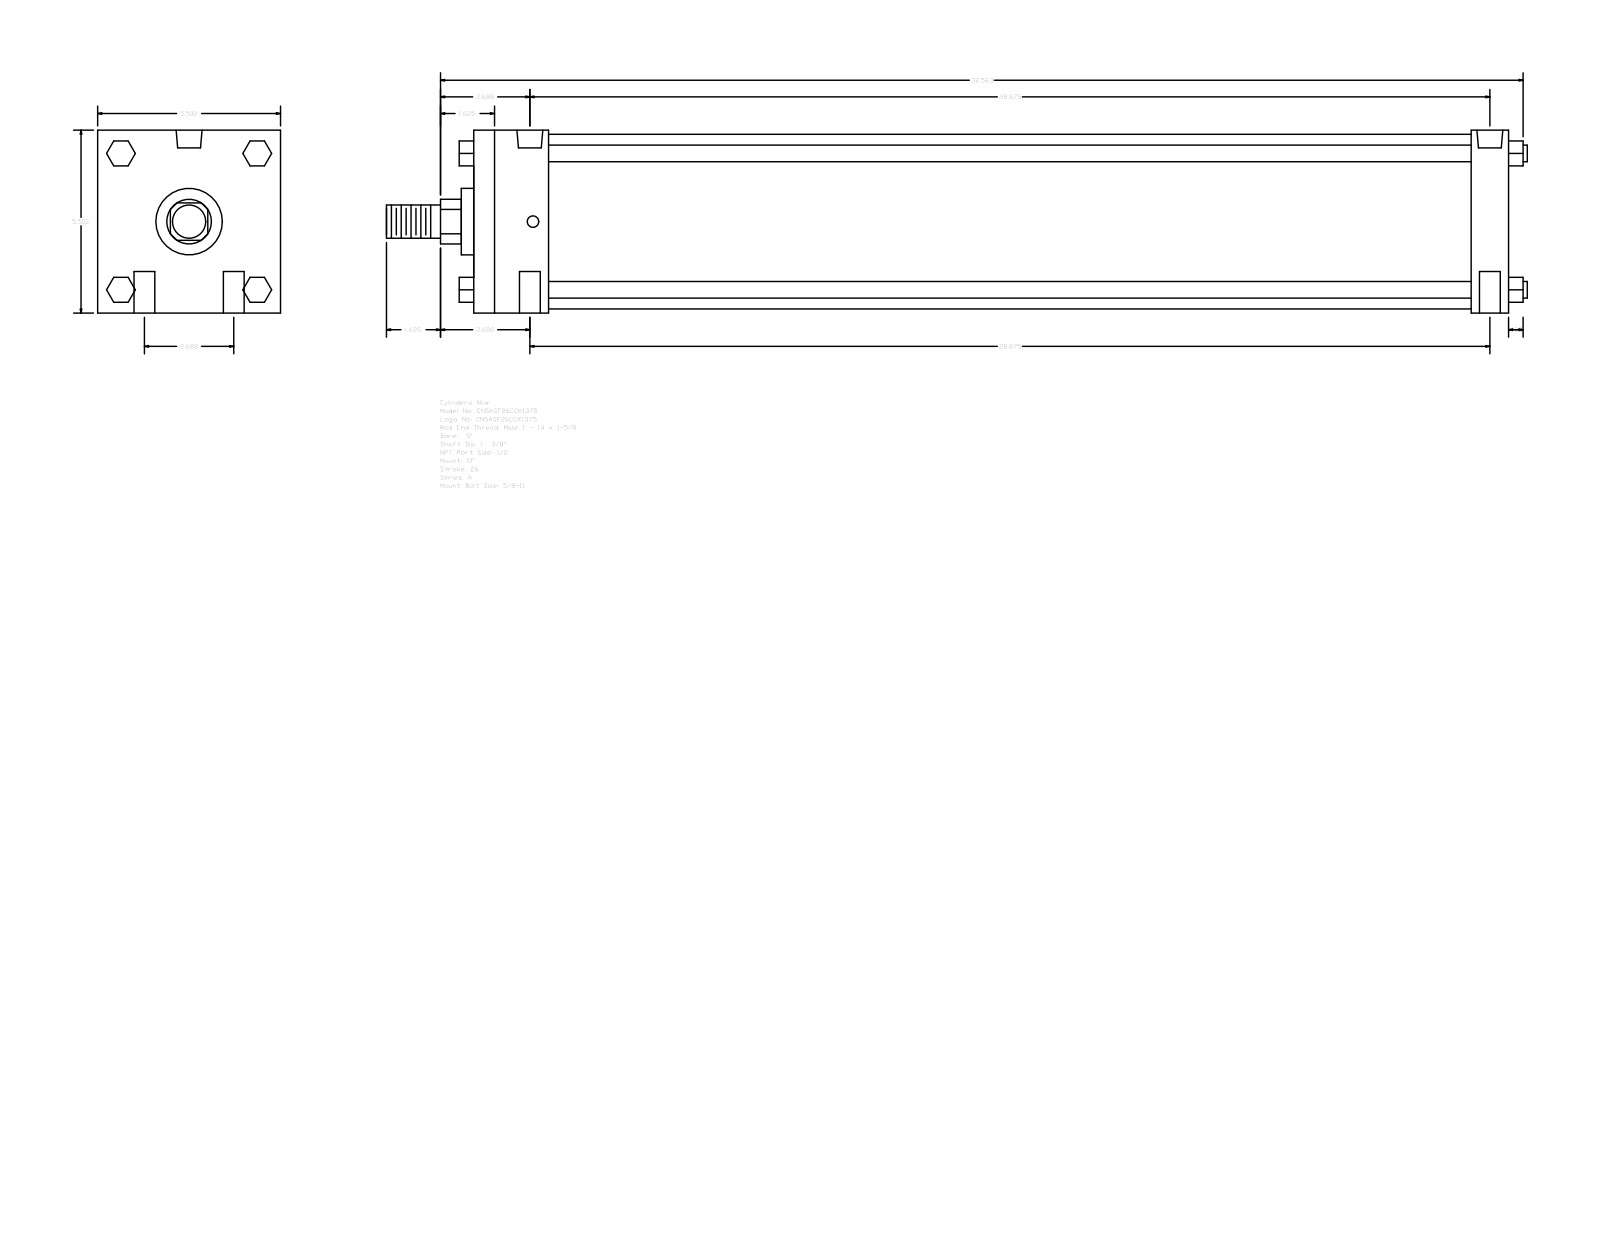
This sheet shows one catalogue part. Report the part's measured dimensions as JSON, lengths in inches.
{"part_name": "A_SF__0500_1.375", "step_written_by": "GSSL Pune (CONFIG_CONTROL_DESIGN)", "units": "inches", "bodies": {"solids": 0, "faces": 124, "planar": 94, "cylindrical": 30, "other": 0}, "overall_size": [34.313, 5.5, 5.5], "round_holes": [[0.625, 4], [0.344, 2], [0.778, 2]], "round_bosses_or_shafts": [[0.5, 4], [5.25, 1], [2, 1], [1.375, 1], [1, 1]], "partial_cylinders_radius": [[0.672, 1]], "face_to_face_distances": [5.5, 31.125, 2.25, 1.125, 30, 27.75, 28.875, 0.75, 2.05, 3.55], "hole_center_spacings": [1.344, 28.906, 28.875, 2.687, 29, 28.687]}
